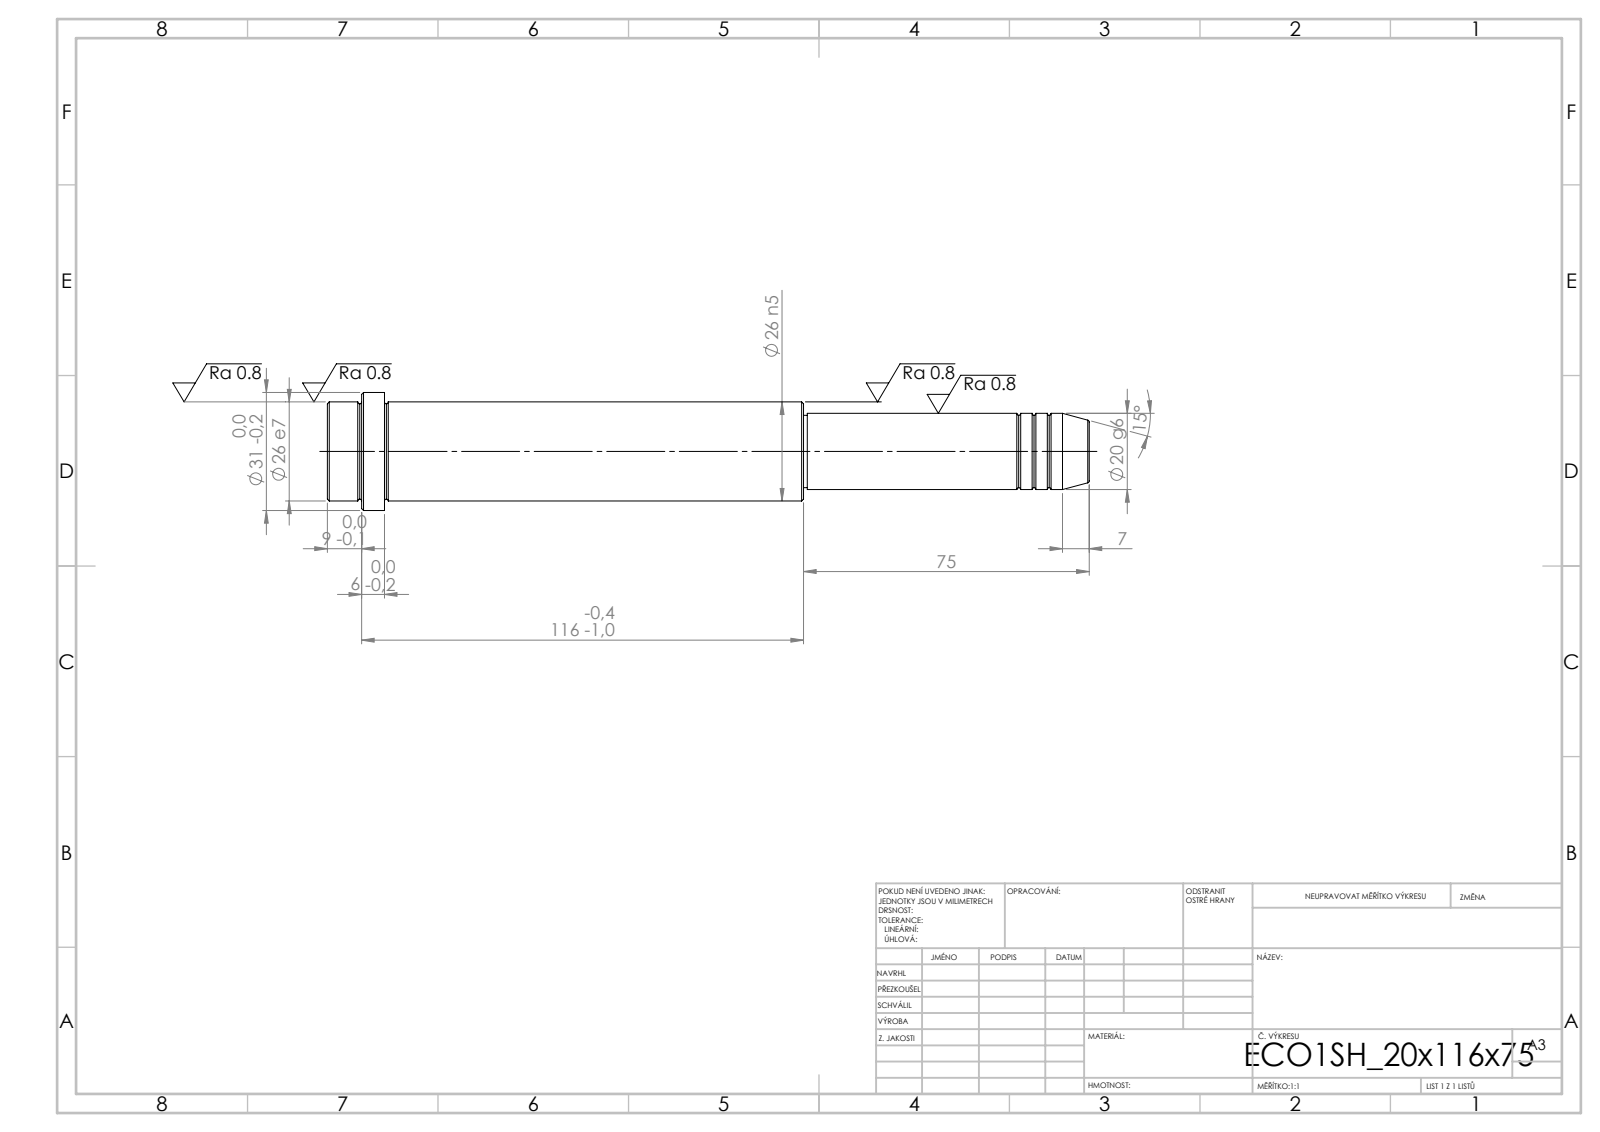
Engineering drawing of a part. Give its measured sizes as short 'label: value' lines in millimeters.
written by: SolidWorks 2019 (CONFIG_CONTROL_DESIGN)
unit: mm
bodies: 1 solid, 52 faces (6 planar, 16 cylindrical, 30 other)
size: 200 × 31 × 31
volume: 90 685 mm³; area: 16 552 mm²
bosses: 1× ⌀31, 1× ⌀26, 1× ⌀20, 1× ⌀19
face distances: 15, 110, 125, 75, 185, 200, 191, 116, 6, 9
